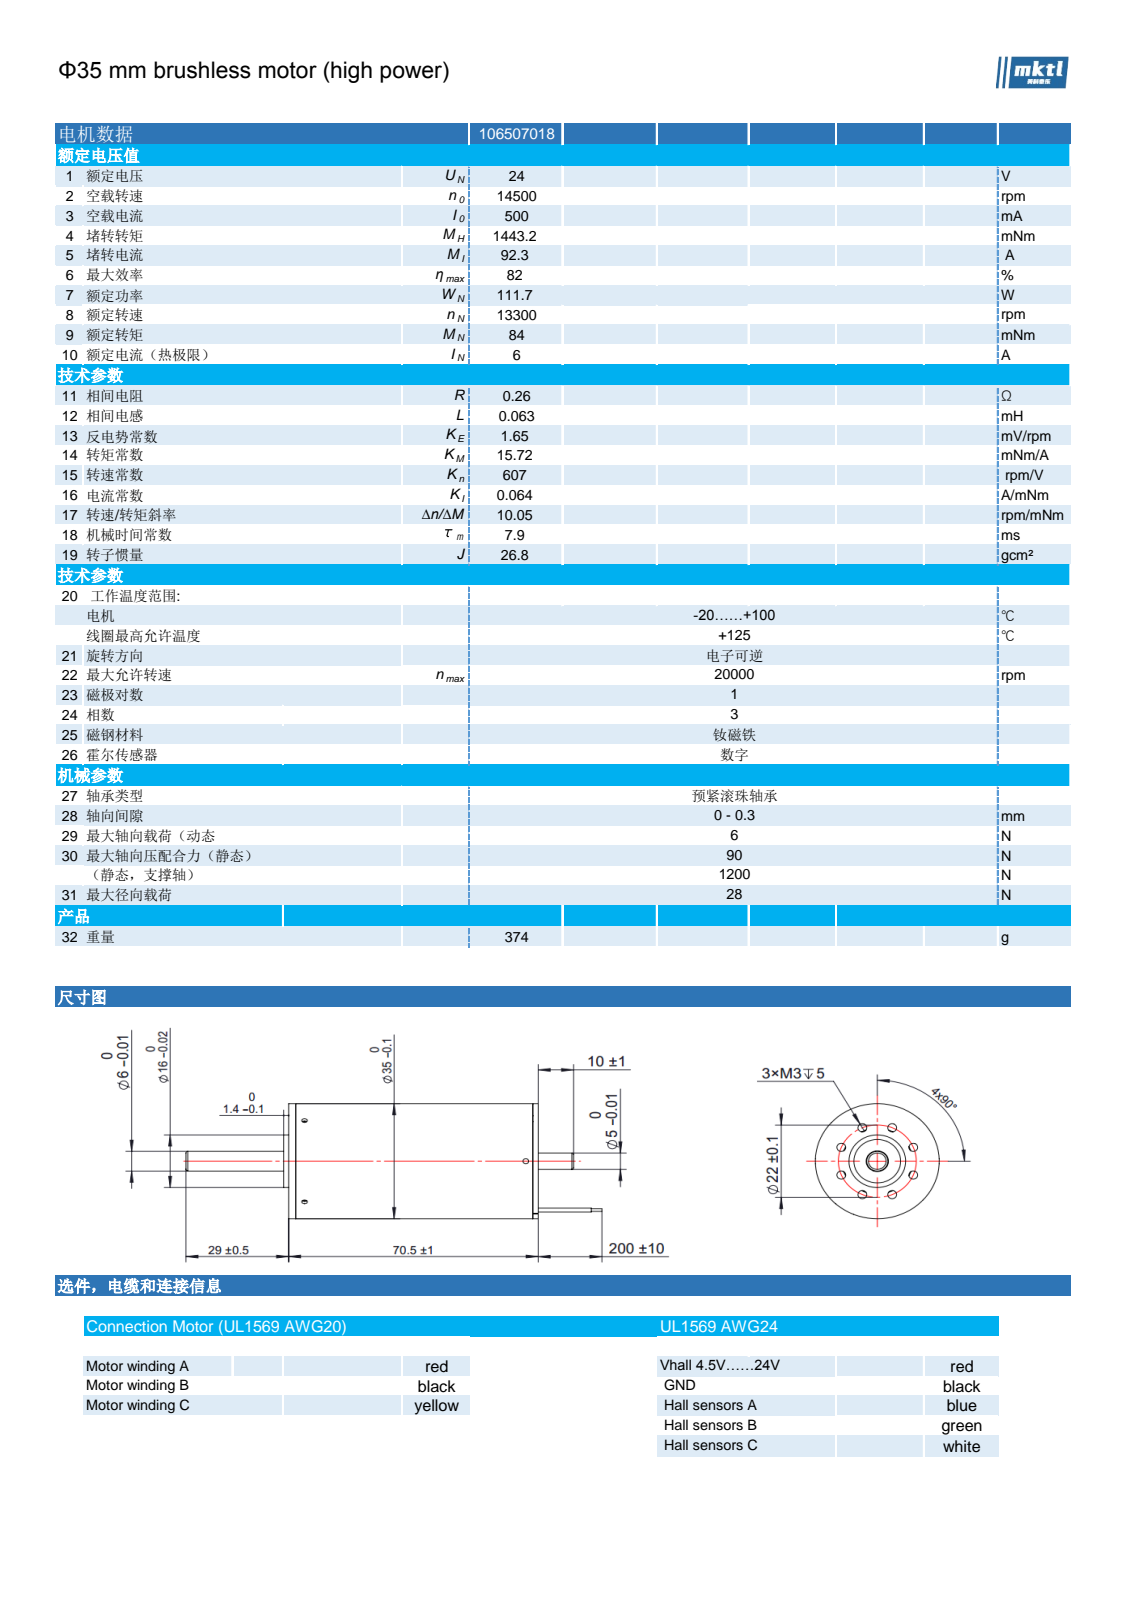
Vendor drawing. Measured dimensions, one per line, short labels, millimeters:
name: 106507018
written by: SolidWorks 2025 (AUTOMOTIVE_DESIGN)
unit: mm
bodies: 324 solids, 2956 faces (1261 planar, 1539 cylindrical, 156 other)
size: 117.5 × 35 × 35
volume: 63 219 mm³; area: 265 100 mm²
holes: 8× ⌀2.5, 6× ⌀2.1, 5× ⌀0.75, 4× ⌀1, 3× ⌀1.5, 3× ⌀1.6, 3× ⌀3, 2× ⌀1.25, 1× ⌀9.5, 1× ⌀10, 1× ⌀13, 1× ⌀13.2
bosses: 6× ⌀0.58, 5× ⌀1, 5× ⌀0.6, 3× ⌀4, 3× ⌀1.6, 3× ⌀1.2, 3× ⌀0.8, 1× ⌀35
rounds: 24× R0.1, 11× R0.75, 8× R0.42, 5× R0.3, 4× R1, 4× R2, 2× R0.5, 1× R4.99
face distances: 0.4, 0.6, 0.8, 1, 1.2, 1.4, 1.6, 1.8, 2, 2.2
hole spacings: 11, 15.55, 20.32, 13.25, 2, 8.41, 8.42, 22
